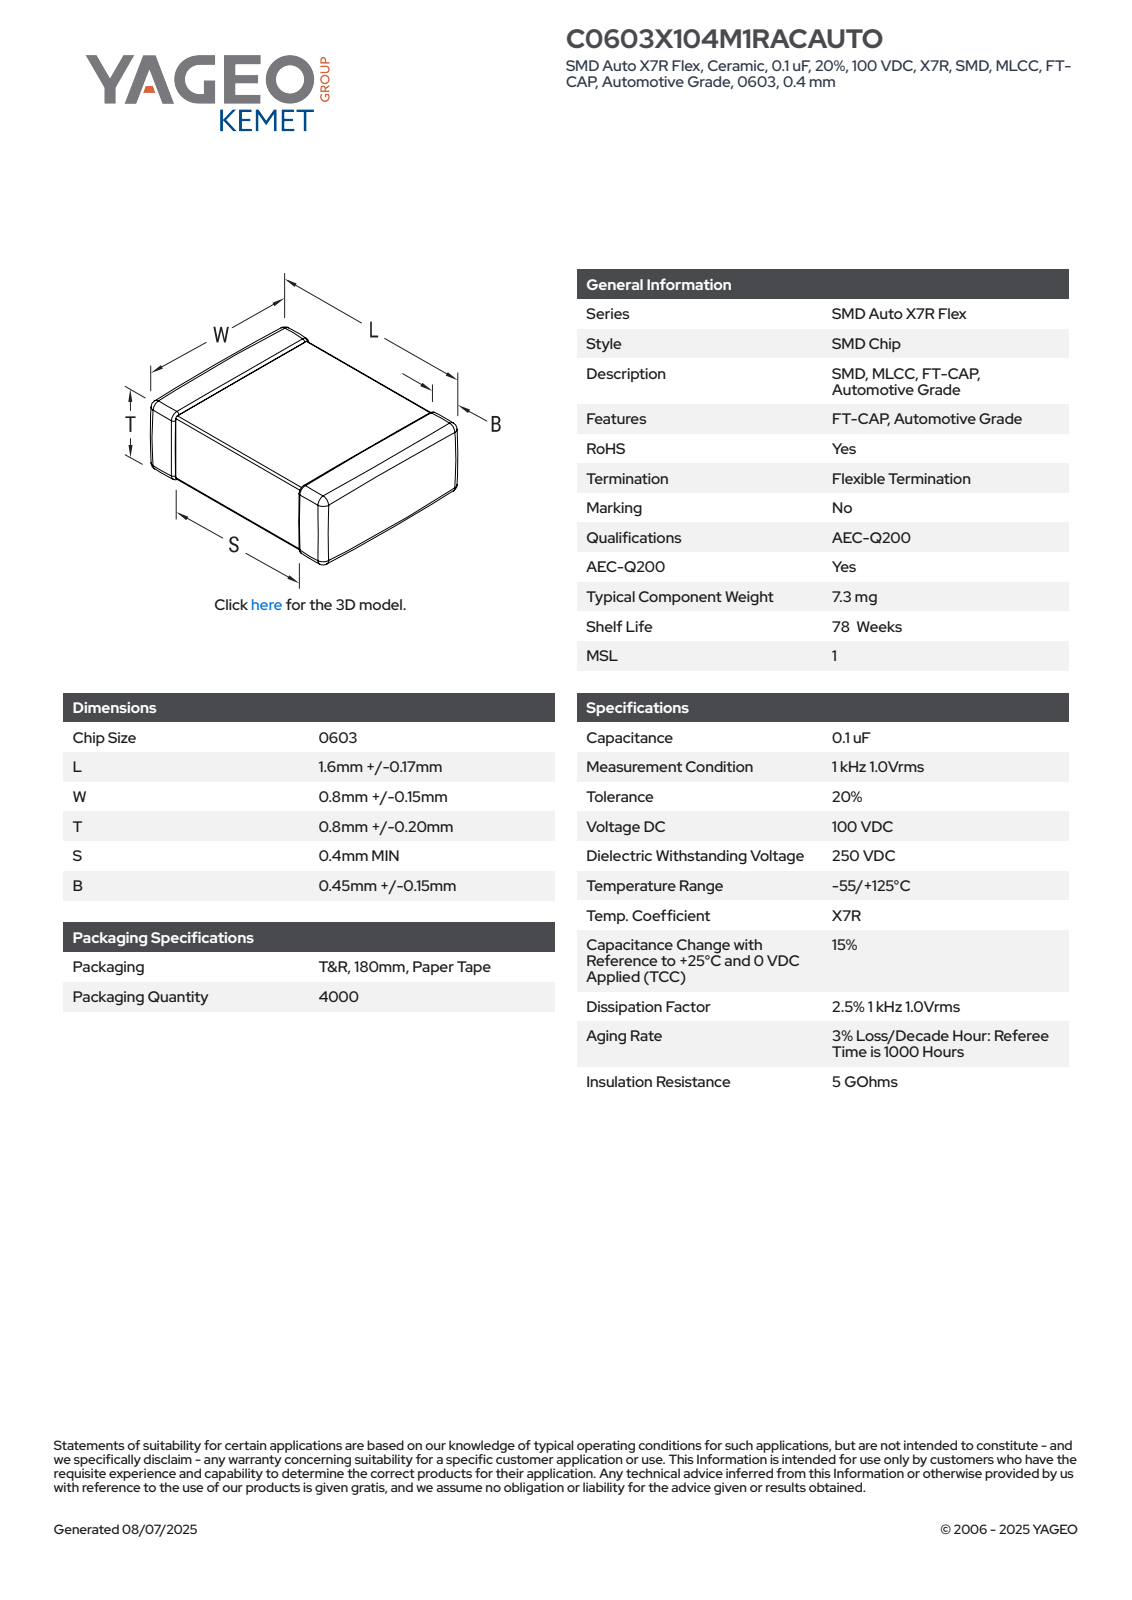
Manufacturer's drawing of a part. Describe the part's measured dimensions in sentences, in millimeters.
The part is named "CCS_CCSTD_0603_L1.77W0.95T1B0.45". Its 3-D file was written by "SolidWorks 2021 (AUTOMOTIVE_DESIGN)". It is 4 solids with 125 faces: 71 planar, 38 cylindrical and 16 other. Overall it measures 1.77 by 1 by 0.95 millimeters. Its volume is 2 cubic millimeters and its surface area 9 square millimeters. The main face-to-face distances are 0.95, 0.93, 0.98, 1, 1.77, 0.91, 0.96, 0.99, 0.97, 0.82.
